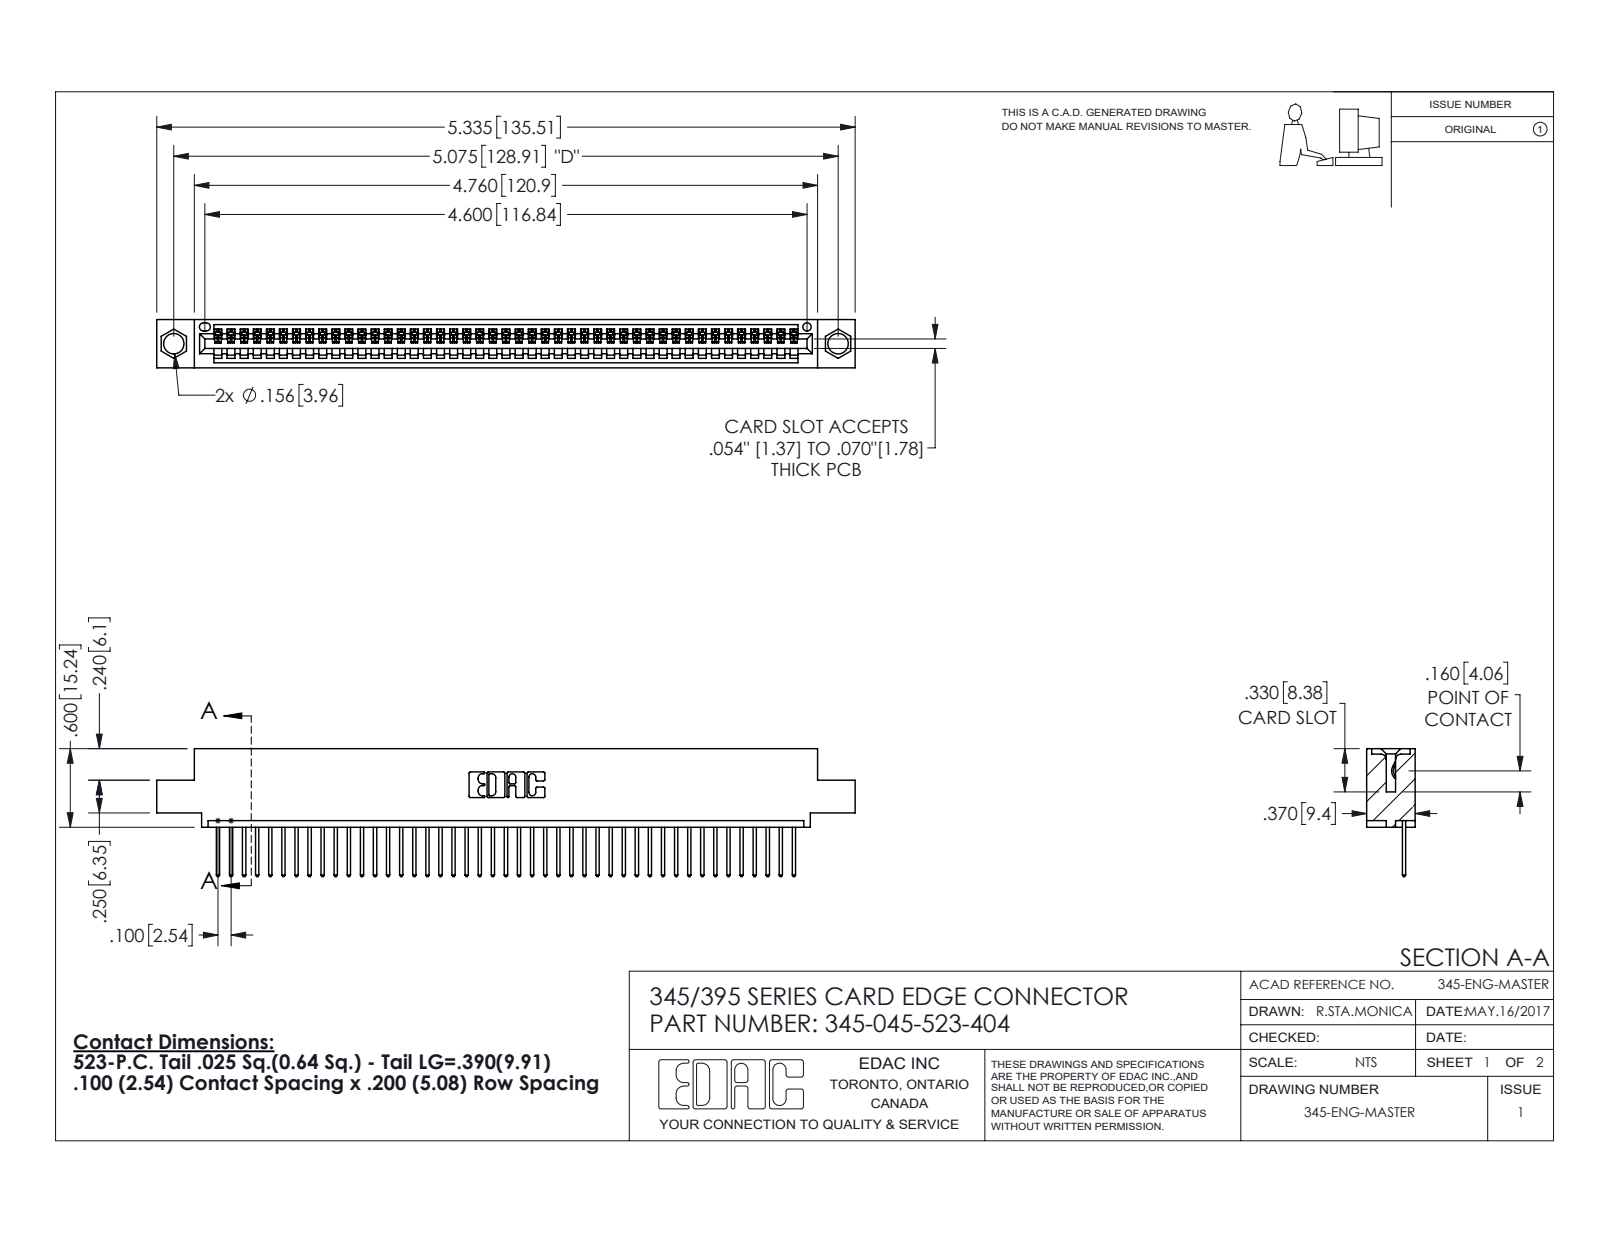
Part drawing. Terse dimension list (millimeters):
name: 345-292-001_345-293-123; 345-045-523-404; 345 Part_0.110 Offset - 0.156 Dia-TH
written by: SolidWorks 2016 (CONFIG_CONTROL_DESIGN)
unit: mm
bodies: 46 solids, 2740 faces (1884 planar, 856 cylindrical, 0 other)
size: 135.5 × 24.8 × 9.4
volume: 12 700 mm³; area: 16 880 mm²
holes: 2× ⌀4, 1× ⌀1.6
rounds: 90× R0.2, 90× R0.3, 22× R0.3, 6× R0.2, 6× R0.8, 3× R0.7, 2× R0.8, 2× R1
face distances: 7.6, 1.8, 9.4, 5.1, 2.5, 6.9, 0.6, 5.7, 3.8, 1.8
hole spacings: 6.9, 122.9, 128.9
